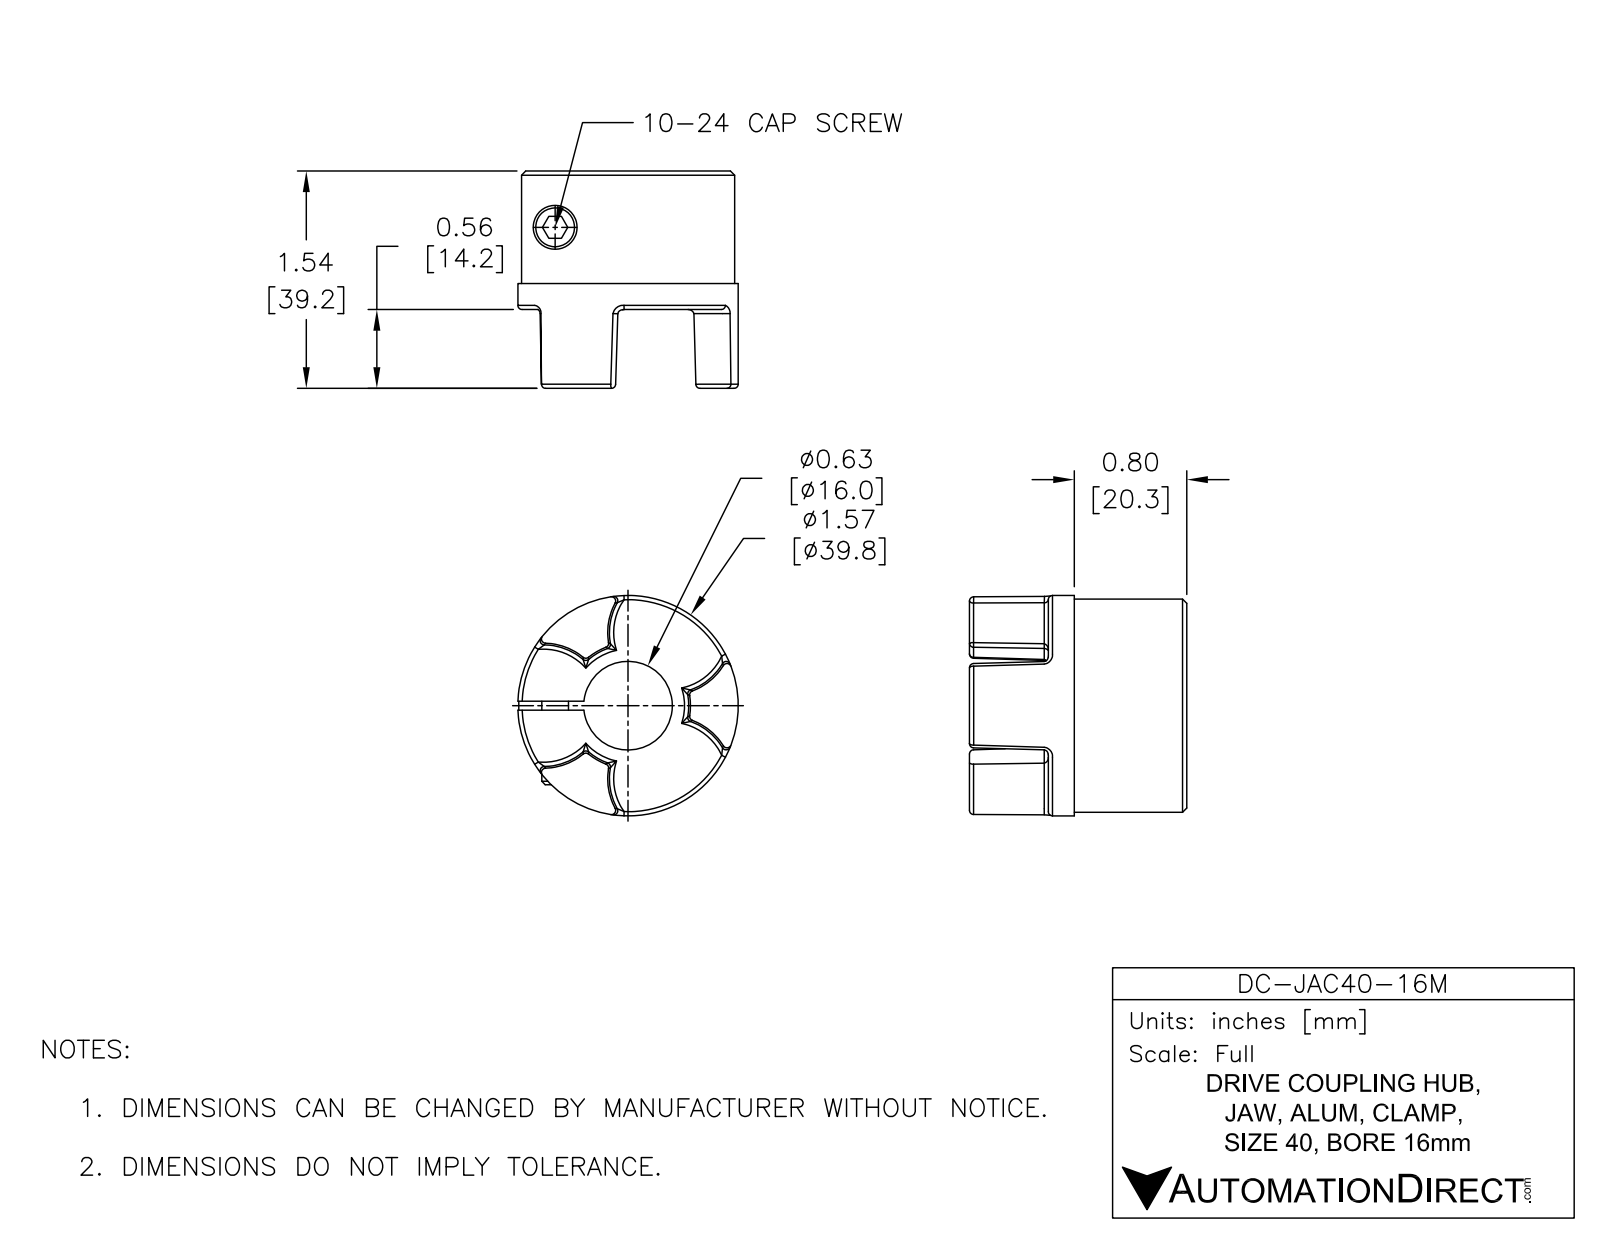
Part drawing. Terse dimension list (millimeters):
name: DC-JAC40-16M
written by: SolidWorks 2015 (AUTOMOTIVE_DESIGN)
unit: mm
bodies: 1 solid, 107 faces (12 planar, 17 cylindrical, 78 other)
size: 39.78 × 39.76 × 39.22
volume: 26 826 mm³; area: 8 733 mm²
holes: 1× ⌀5.11, 1× ⌀8.36, 1× ⌀16
bosses: 1× ⌀39.78, 1× ⌀38.48
rounds: 2× R0.76
face distances: 24.99, 1.6, 39.22, 14.23, 20.29, 4.7, 18.93, 3.99, 5.59
